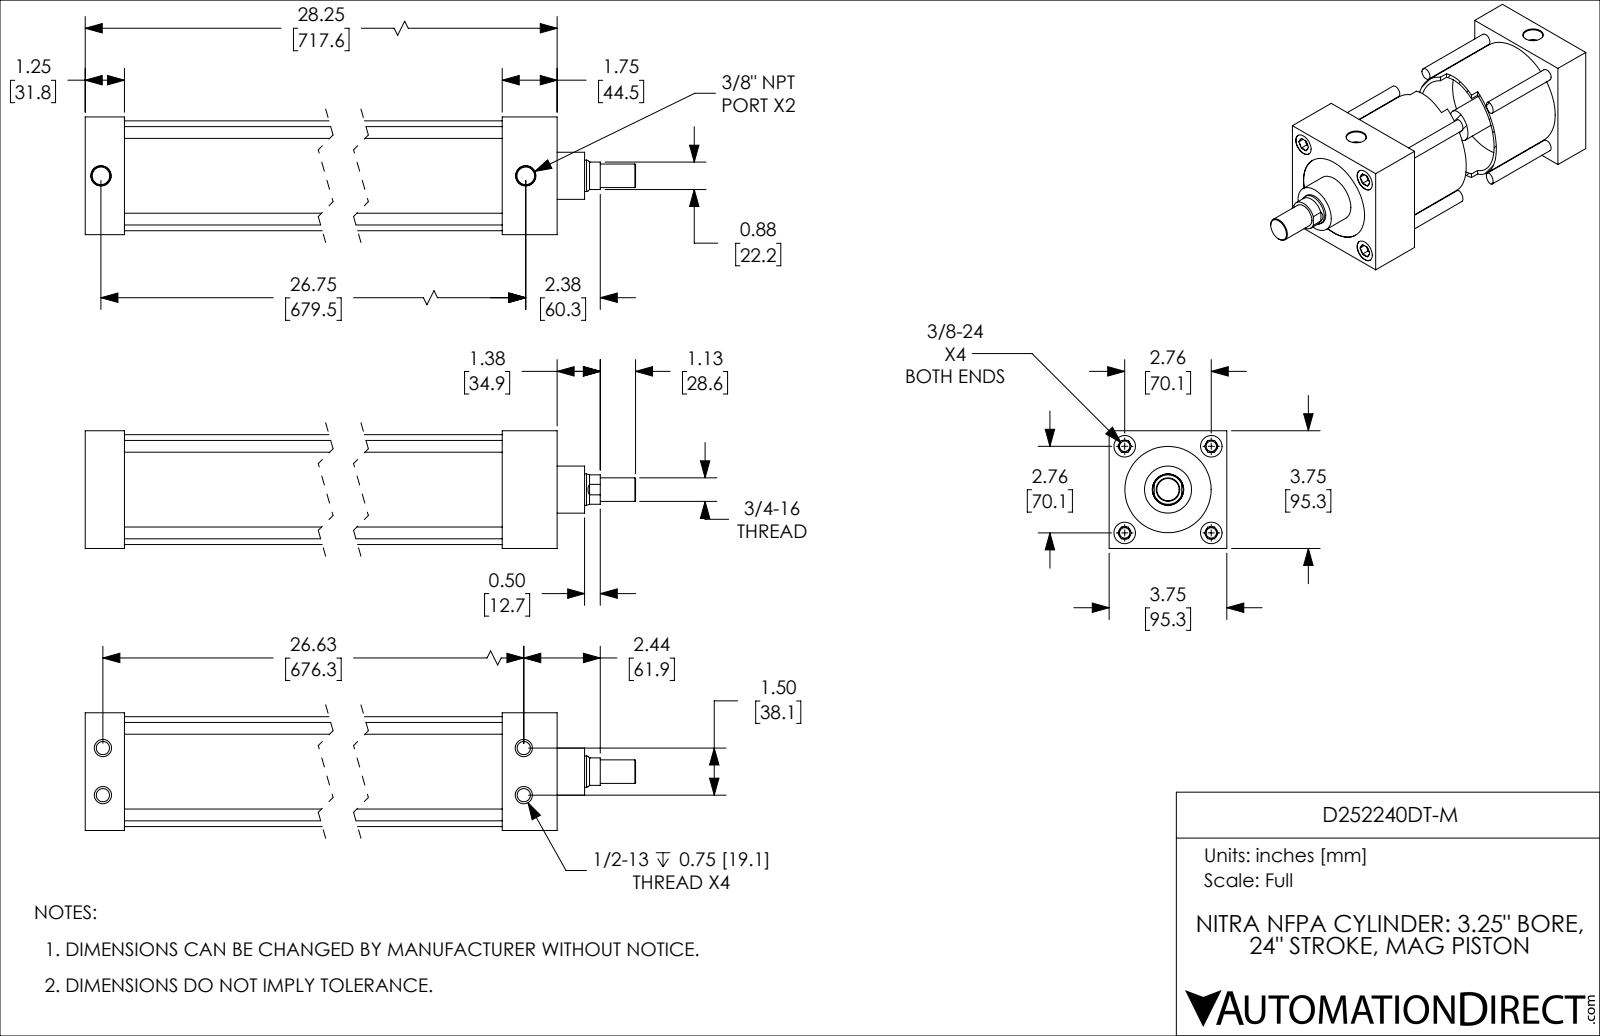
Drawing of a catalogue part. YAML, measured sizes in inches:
part_name: "D252240DT-M; D252240DT-M_BODY; D252240DT-M_PISTON_KK1"
step_written_by: "SolidWorks 2019 (CONFIG_CONTROL_DESIGN)"
units: inches
bodies: {solids: 2, faces: 198, planar: 58, cylindrical: 62, other: 78}
overall_size: [30.75, 3.75, 3.75]
volume: 116.2
surface_area: 898.9
round_holes:
  - {diameter: 0.332, count: 4}
  - {diameter: 0.422, count: 4}
  - {diameter: 0.687, count: 4}
  - {diameter: 0.562, count: 2}
  - {diameter: 1, count: 1}
  - {diameter: 2.75, count: 1}
  - {diameter: 3.251, count: 1}
round_bosses_or_shafts:
  - {diameter: 0.375, count: 4}
  - {diameter: 3.501, count: 1}
  - {diameter: 3.249, count: 1}
  - {diameter: 1.5, count: 1}
  - {diameter: 0.999, count: 1}
  - {diameter: 0.75, count: 1}
partial_cylinders:
  - {radius: 0.469, count: 1}
face_to_face_distances: [1.25, 3.75, 26.5, 25.25, 2.5, 24, 28.25, 27, 25.75, 1.75]
hole_center_spacings: [0.753, 1.952, 2.76, 26.698, 1.5, 3.903, 26.625, 26.667]
